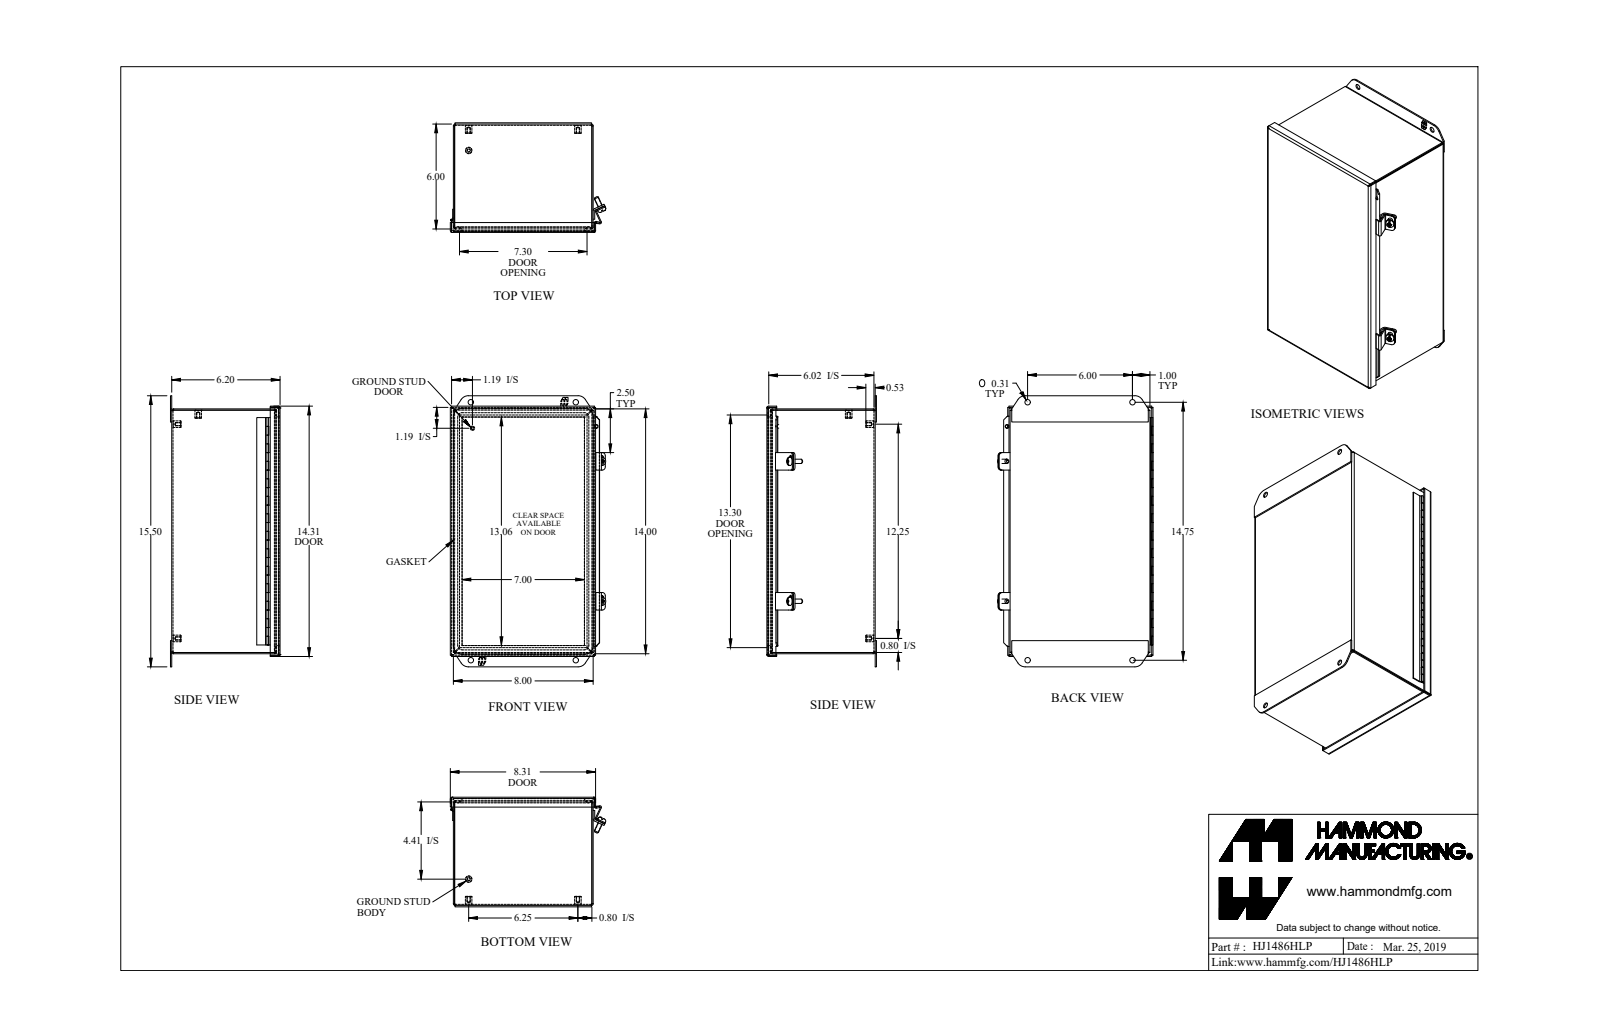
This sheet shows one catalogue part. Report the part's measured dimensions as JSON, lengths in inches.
{"part_name": "HJ1486HLP", "step_written_by": "SolidWorks 2018 (AUTOMOTIVE_DESIGN)", "units": "inches", "bodies": {"solids": 20, "faces": 809, "planar": 430, "cylindrical": 251, "other": 128}, "overall_size": [15.5, 8.896, 6.269], "volume_in3": 44.57, "surface_area_in2": 1256, "round_holes": [[0.156, 5], [0.313, 4], [0.213, 2], [0.05, 1]], "round_bosses_or_shafts": [[0.375, 5], [0.25, 3], [0.48, 2], [0.188, 1], [0.1, 1], [0.045, 1]], "partial_cylinders_radius": [[0.25, 16], [0.036, 13], [0.108, 13], [0.188, 8], [0.01, 4], [0.141, 4], [0.499, 4], [0.5, 4]], "face_to_face_distances": [0.072, 6.125, 7.928, 6.197, 6.053, 13.928, 8, 7.856, 14, 13.856], "hole_center_spacings": [14.824, 1.256, 1.257, 6, 6.25, 6.251, 6.252, 12.25]}
